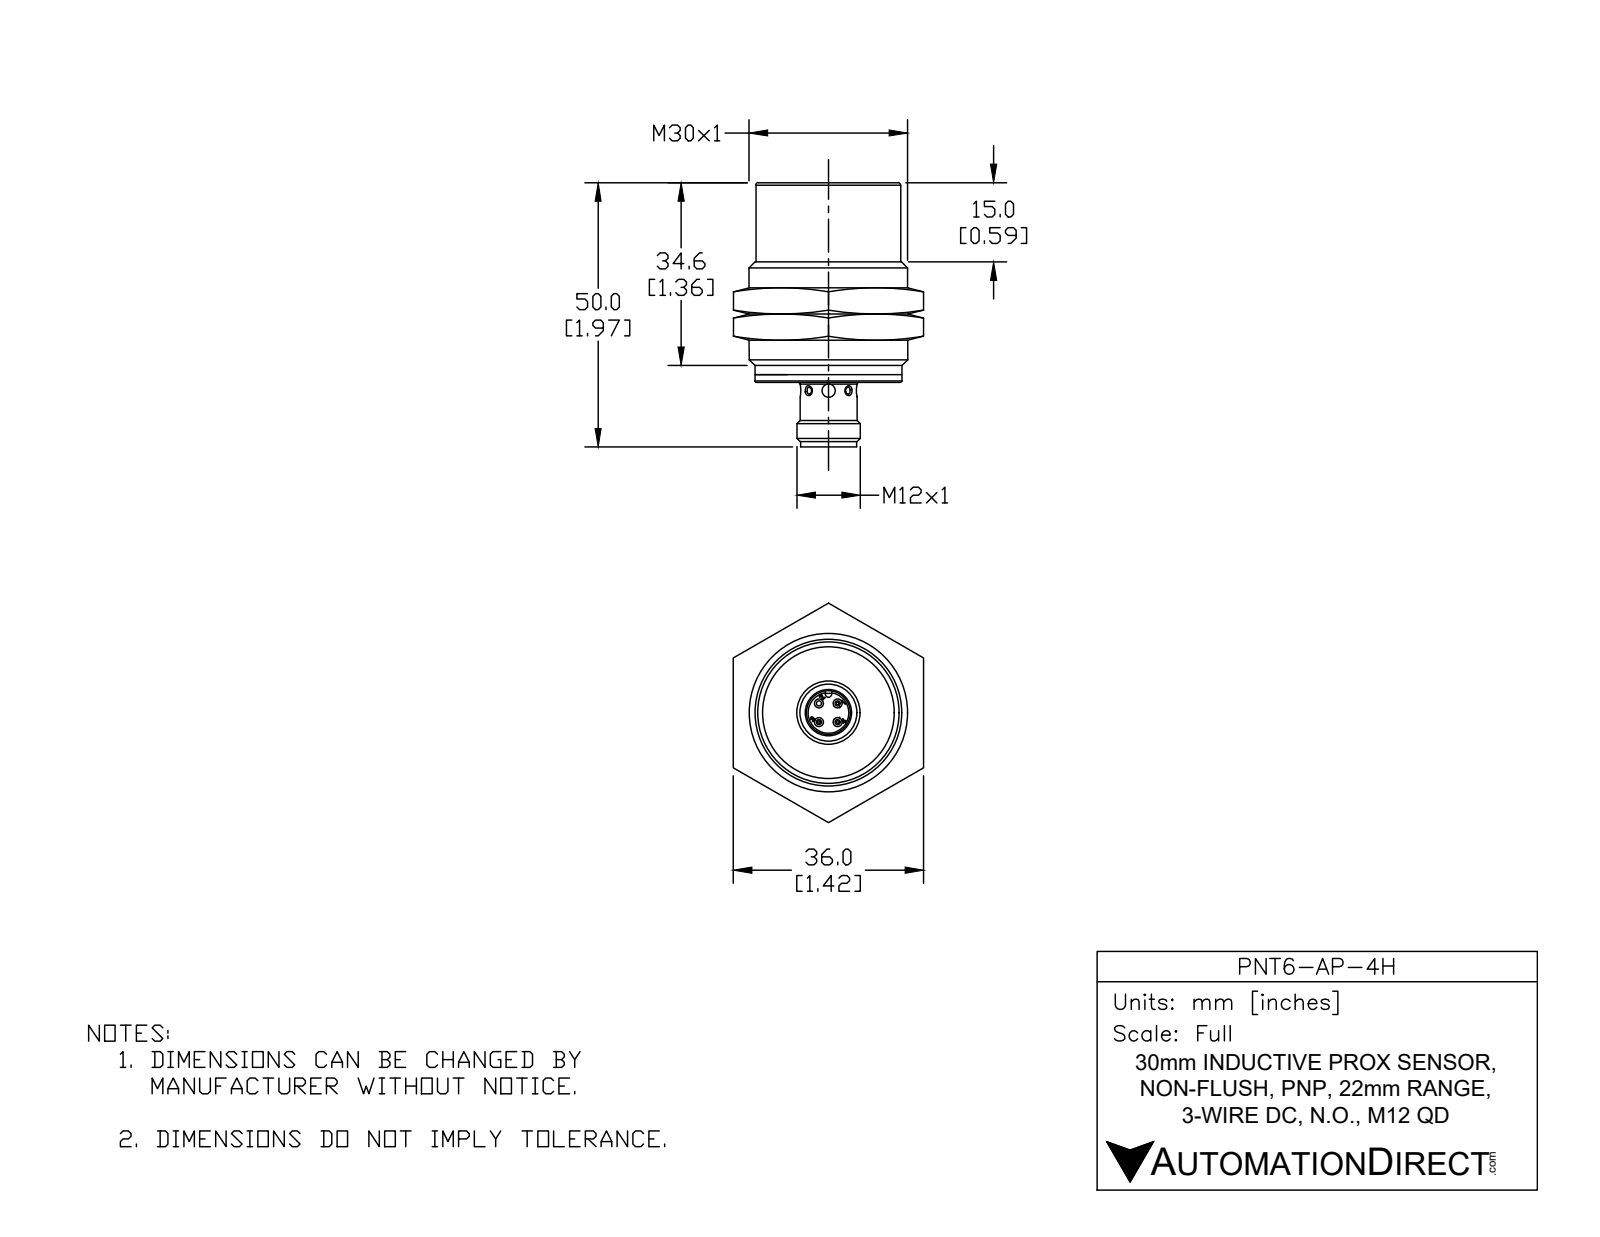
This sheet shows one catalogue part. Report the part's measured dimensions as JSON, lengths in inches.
{"part_name": "PNT6-AP-4H", "step_written_by": "SolidWorks 2017 (AUTOMOTIVE_DESIGN)", "units": "inches", "bodies": {"solids": 1, "faces": 515, "planar": 161, "cylindrical": 130, "other": 224}, "overall_size": [1.969, 1.181, 1.181], "volume_in3": 1.573, "surface_area_in2": 12.79, "round_holes": [[0.043, 3], [0.04, 2], [0.098, 2], [0.038, 1], [0.04, 1], [0.323, 1], [0.327, 1], [0.394, 1], [1.047, 1], [1.076, 1], [1.089, 1]], "round_bosses_or_shafts": [[0.039, 9], [1.181, 1], [1.094, 1], [1.083, 1], [1.074, 1], [1.044, 1], [0.878, 1], [0.472, 1]], "partial_cylinders_radius": [[0.004, 12], [0.02, 8], [0.03, 3], [0.039, 3], [0.024, 1], [0.031, 1]], "face_to_face_distances": [0.126, 1.488, 1.362, 0.037, 0.089, 1.451, 0.098, 1.461, 0.028, 0.024], "hole_center_spacings": [0.098, 0.139, 0.197]}
